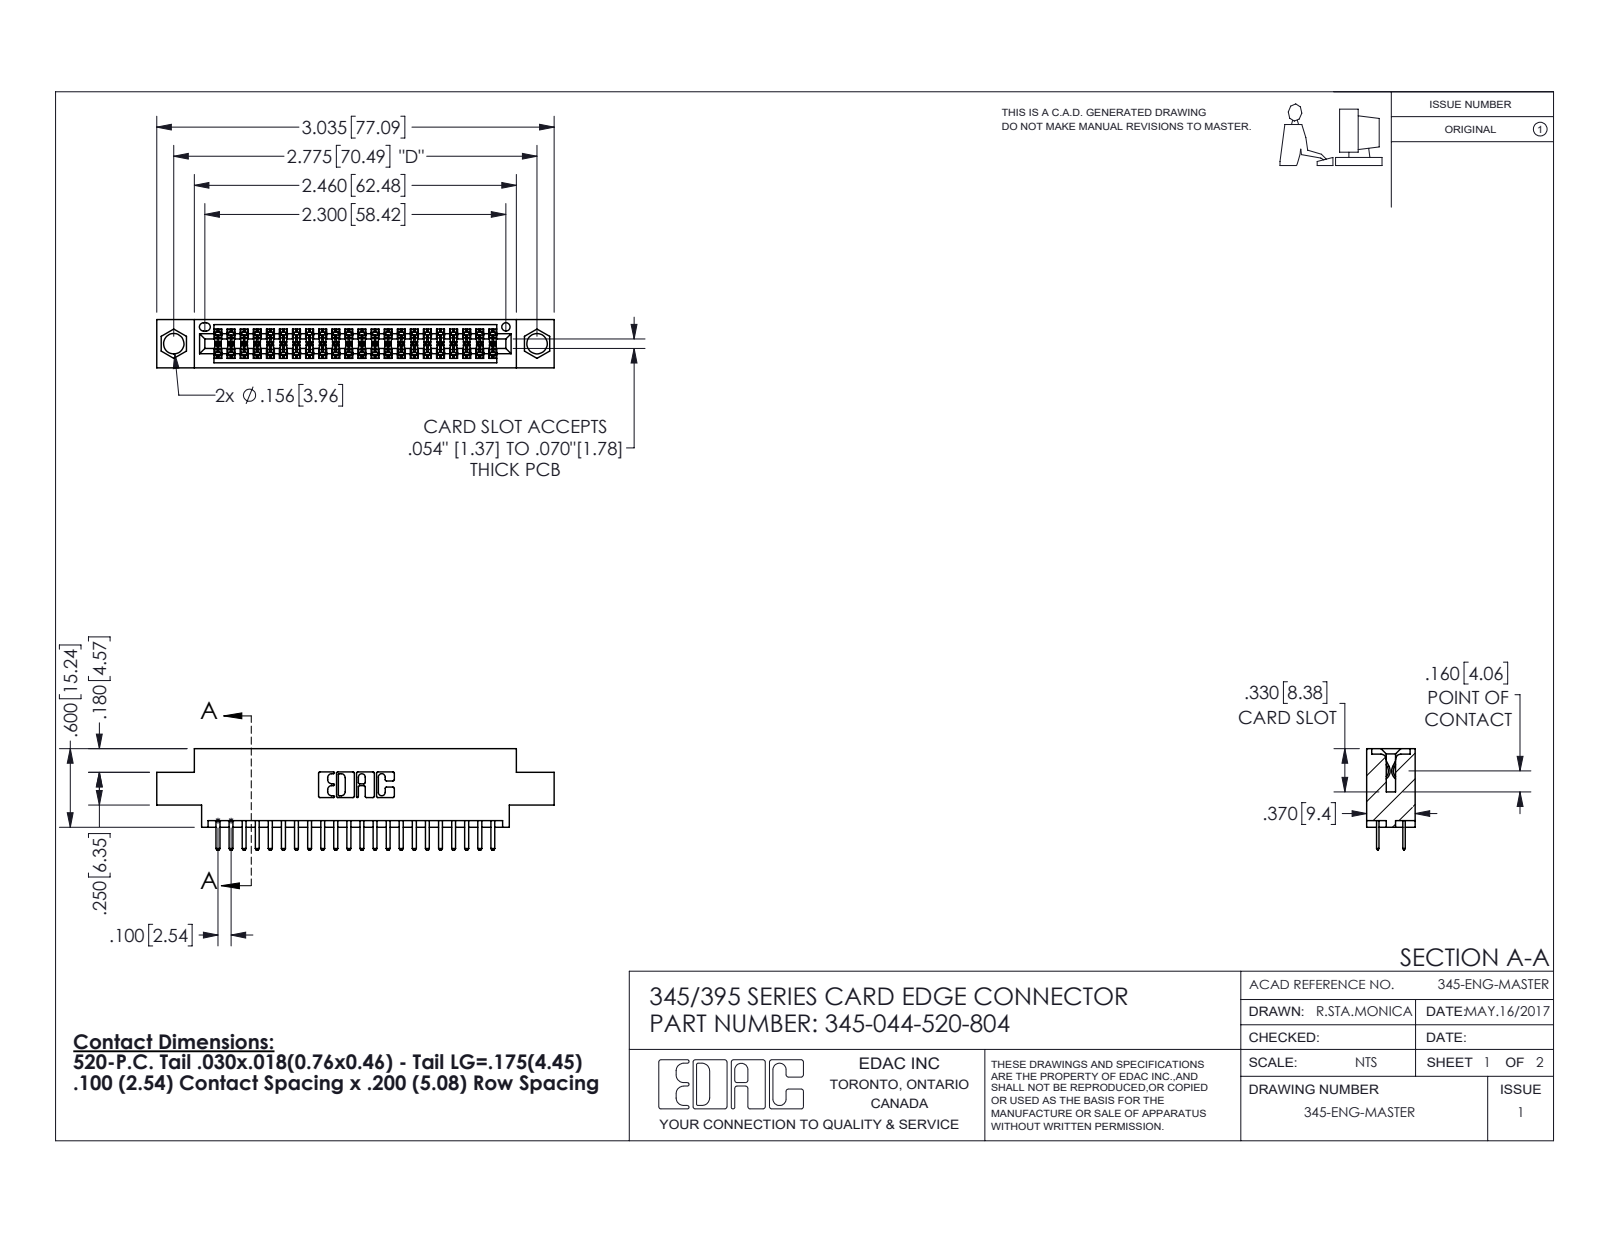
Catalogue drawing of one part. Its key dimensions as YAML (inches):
part_name: "345-292-001_345-293-120; 345 Part_0.170 Offset - 0.156 Dia-TI; 345-044-520-804"
step_written_by: "SolidWorks 2020 (CONFIG_CONTROL_DESIGN)"
units: inches
bodies: {solids: 45, faces: 2520, planar: 1638, cylindrical: 882, other: 0}
overall_size: [3.035, 0.775, 0.37]
volume: 0.431
surface_area: 15.51
round_holes:
  - {diameter: 0.156, count: 2}
  - {diameter: 0.064, count: 1}
partial_cylinders:
  - {radius: 0.006, count: 66}
  - {radius: 0.01, count: 48}
  - {radius: 0.01, count: 22}
  - {radius: 0.007, count: 6}
  - {radius: 0.031, count: 6}
  - {radius: 0.026, count: 3}
  - {radius: 0.014, count: 2}
  - {radius: 0.019, count: 2}
face_to_face_distances: [0.072, 0.298, 0.2, 0.37, 0.098, 0.272, 0.025, 0.225, 0.022, 0.175]
hole_center_spacings: [0.27, 2.541, 2.775]
